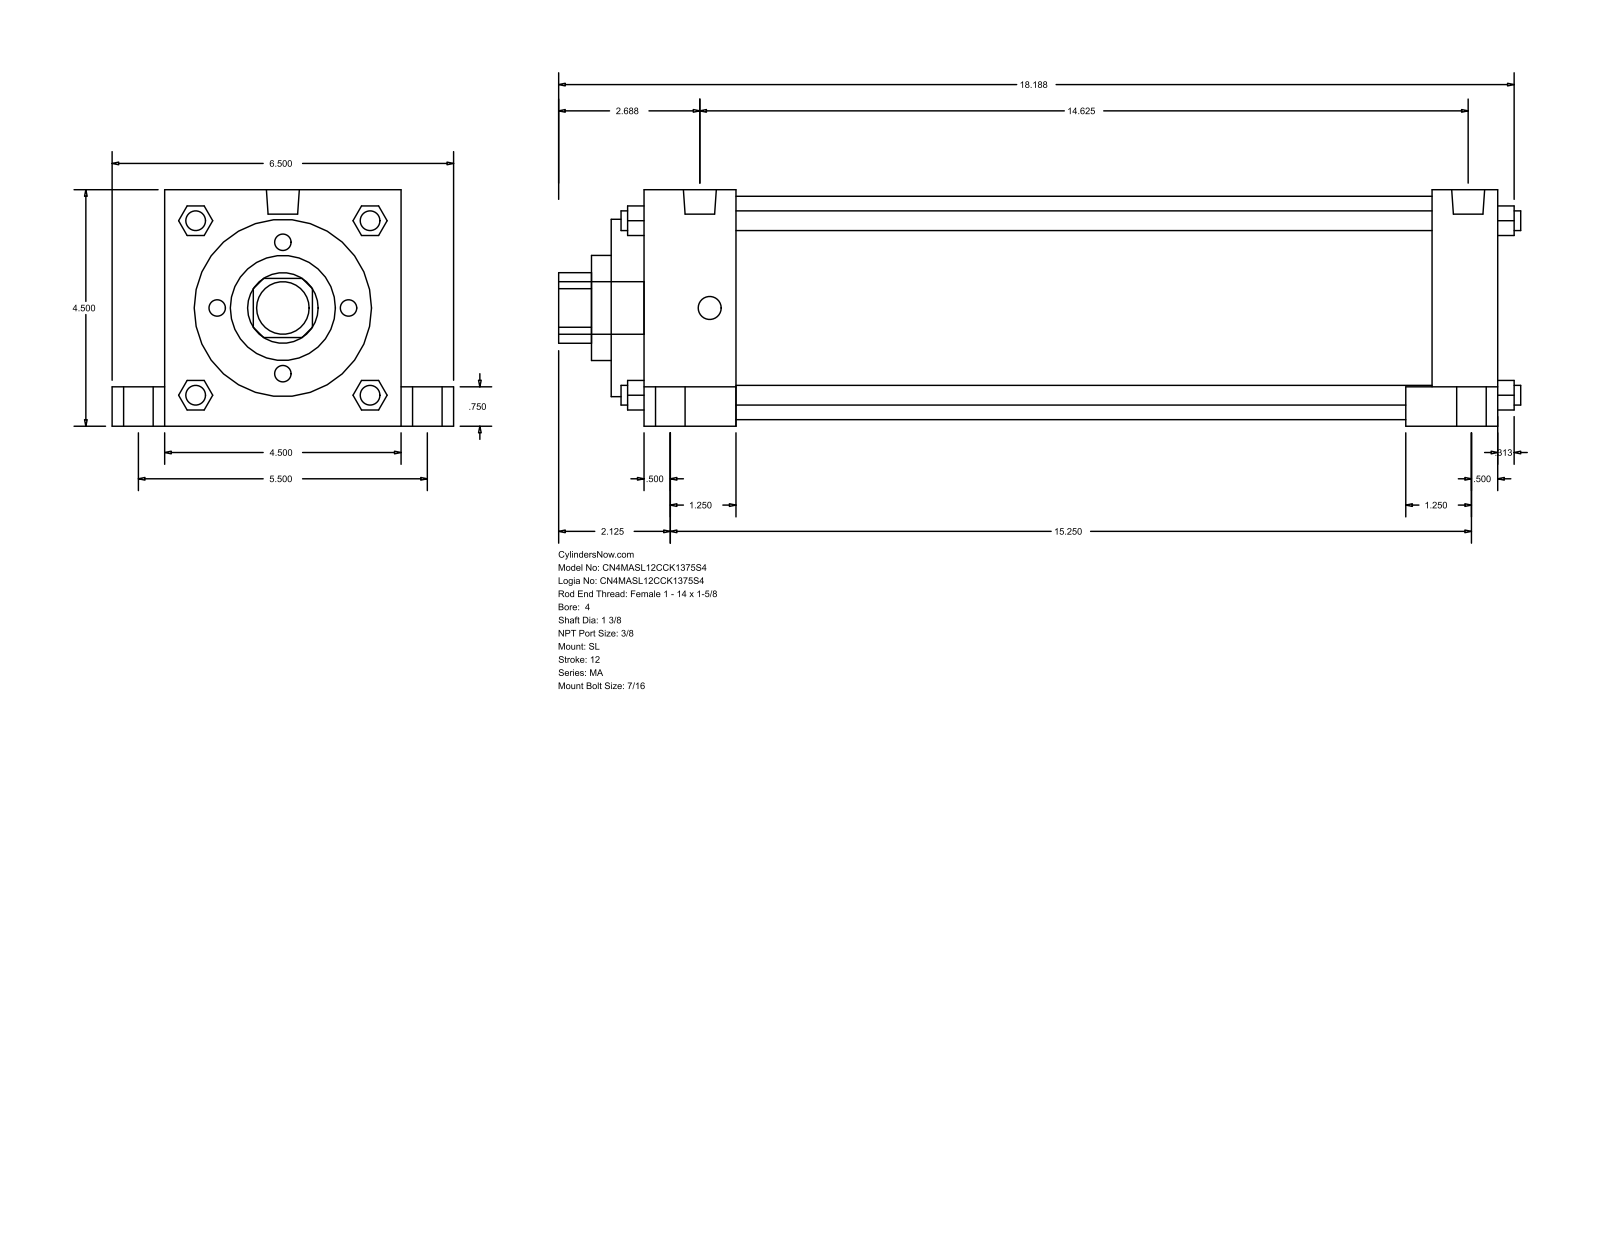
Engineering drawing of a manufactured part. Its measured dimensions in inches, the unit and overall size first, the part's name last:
Units: inches
Overall size (bounding box): 18.313 × 6.5 × 4.5
Round holes (diameter × count): ⌀1.375 ×1, ⌀2 ×1, ⌀3.375 ×1, ⌀4.25 ×1
Round bosses / shafts (diameter × count): ⌀0.813 ×4, ⌀0.563 ×4, ⌀0.437 ×4, ⌀0.375 ×4, ⌀0.627 ×2, ⌀1 ×1
Partial cylindrical surfaces — rounded edges, fillets, slot ends (radius × count): R0.672 ×1
Main face-to-face distances: 4.5, 16.25, 13.25, 16.875, 0.625, 2.375, 1.75, 14.5, 15.625, 15
Bodies: 0 solids, 150 faces (113 planar, 37 cylindrical, 0 other)
Part name (STEP PRODUCT): MA_SL__0400_1.375
STEP written by: GSSL Pune (CONFIG_CONTROL_DESIGN)
